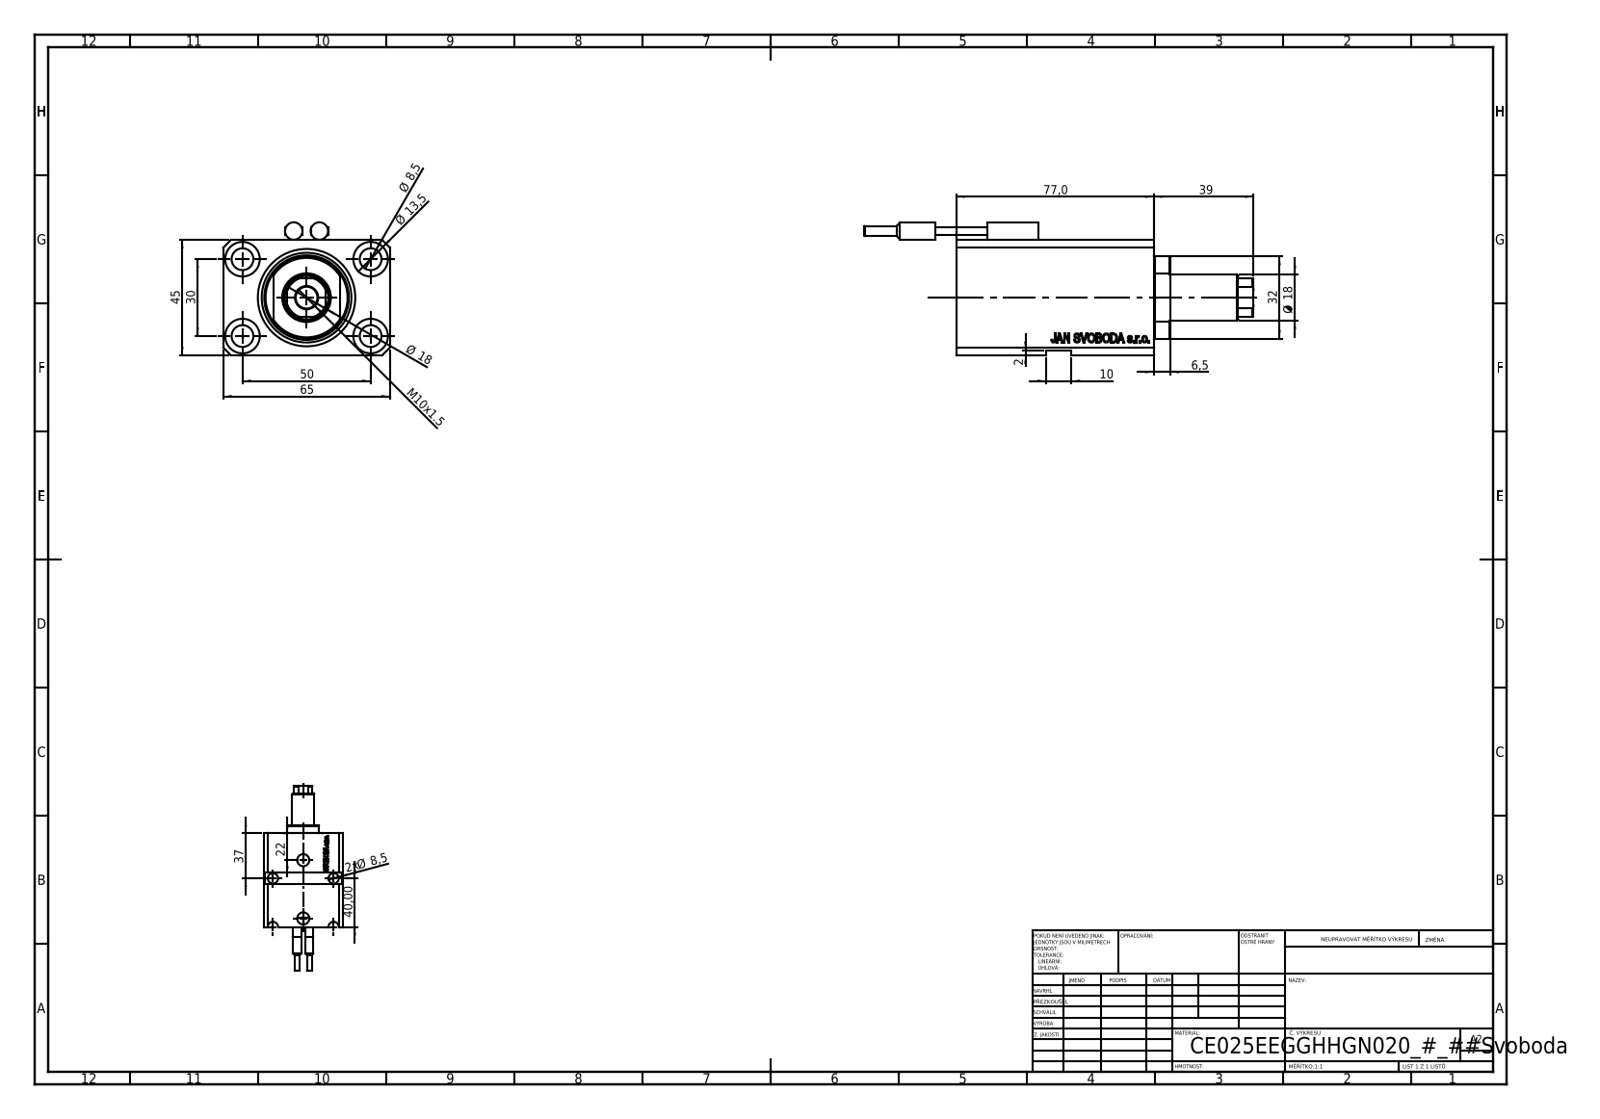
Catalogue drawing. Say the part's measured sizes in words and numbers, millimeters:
The part is named "V250CE_VC_E; V250CE_C_VCP; V250CE_E_Body; SWITCH_V250CE". Its 3-D file was written by "SolidWorks 2019 (CONFIG_CONTROL_DESIGN)". It is 5 solids with 942 faces: 466 planar, 90 cylindrical and 386 other. Overall it measures 152 by 65 by 51.9 millimeters. Its volume is 210 105 cubic millimeters and its surface area 53 901 square millimeters. Round holes: 7 of diameter 8.5, 4 of diameter 13.5, 2 of diameter 1.25, 2 of diameter 10, 1 of diameter 18, 1 of diameter 25, 1 of diameter 38. Round bosses or shafts: 2 of diameter 6.8, 2 of diameter 6.5, 2 of diameter 4. Partial cylindrical surfaces (rounded edges, fillets, slot ends): 2 of radius 4.25, 1 of radius 8.5, 1 of radius 16. The main face-to-face distances are 45, 65, 51.9, 77, 25.1, 32, 19.9, 2, 68, 9. The hole center spacings are 29.15, 50, 30, 40.98, 41.4, 58.31, 0.53, 47.47.
